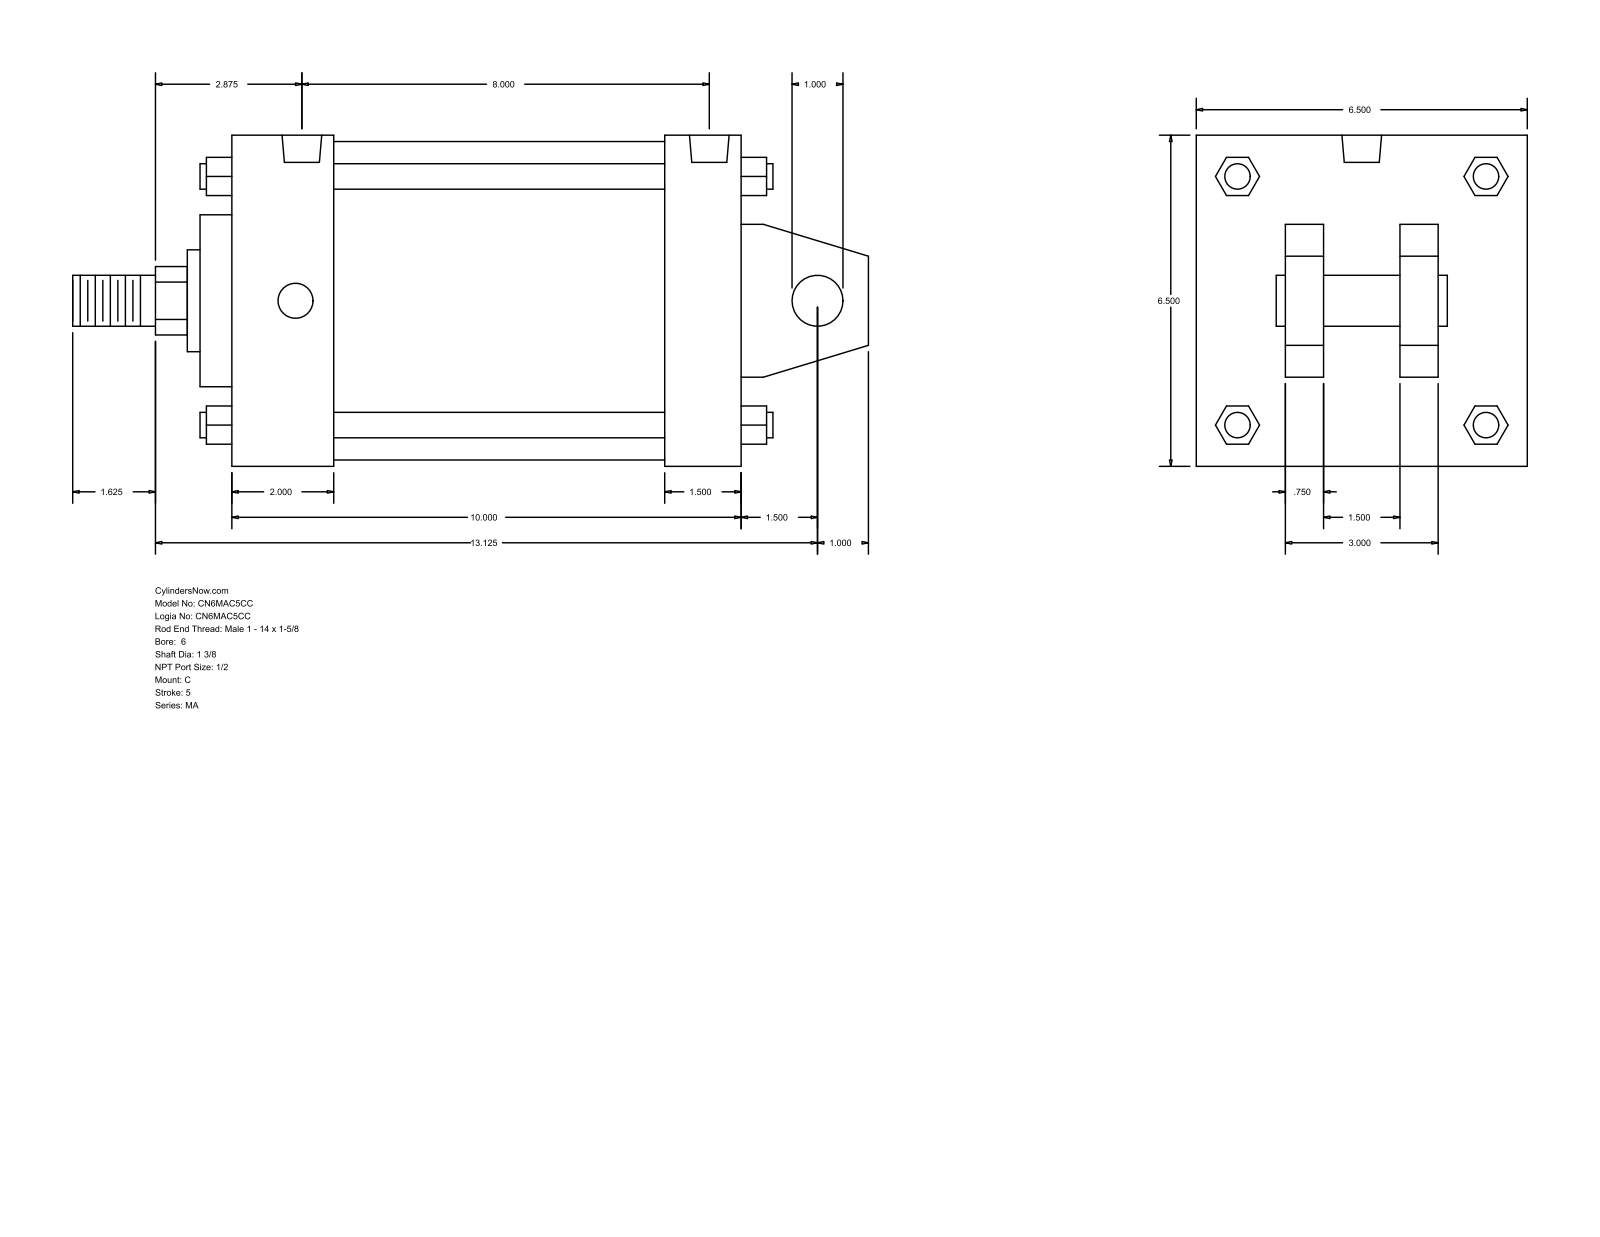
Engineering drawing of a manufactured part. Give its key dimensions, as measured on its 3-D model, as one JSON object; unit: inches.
{"part_name": "MA_C__0600_1.375", "step_written_by": "GSSL Pune (CONFIG_CONTROL_DESIGN)", "units": "inches", "bodies": {"solids": 0, "faces": 141, "planar": 109, "cylindrical": 32, "other": 0}, "overall_size": [15.625, 6.5, 6.5], "round_holes": [[0.687, 4], [0.778, 2]], "round_bosses_or_shafts": [[0.5, 4], [1, 2], [6.25, 1], [3.375, 1], [2, 1], [1.375, 1]], "partial_cylinders_radius": [[0.672, 1]], "face_to_face_distances": [6.5, 10, 1.5, 0.75, 2.5, 4, 2, 1.75, 4.75, 8.5], "hole_center_spacings": [8, 0.125, 7.875, 8.125]}
